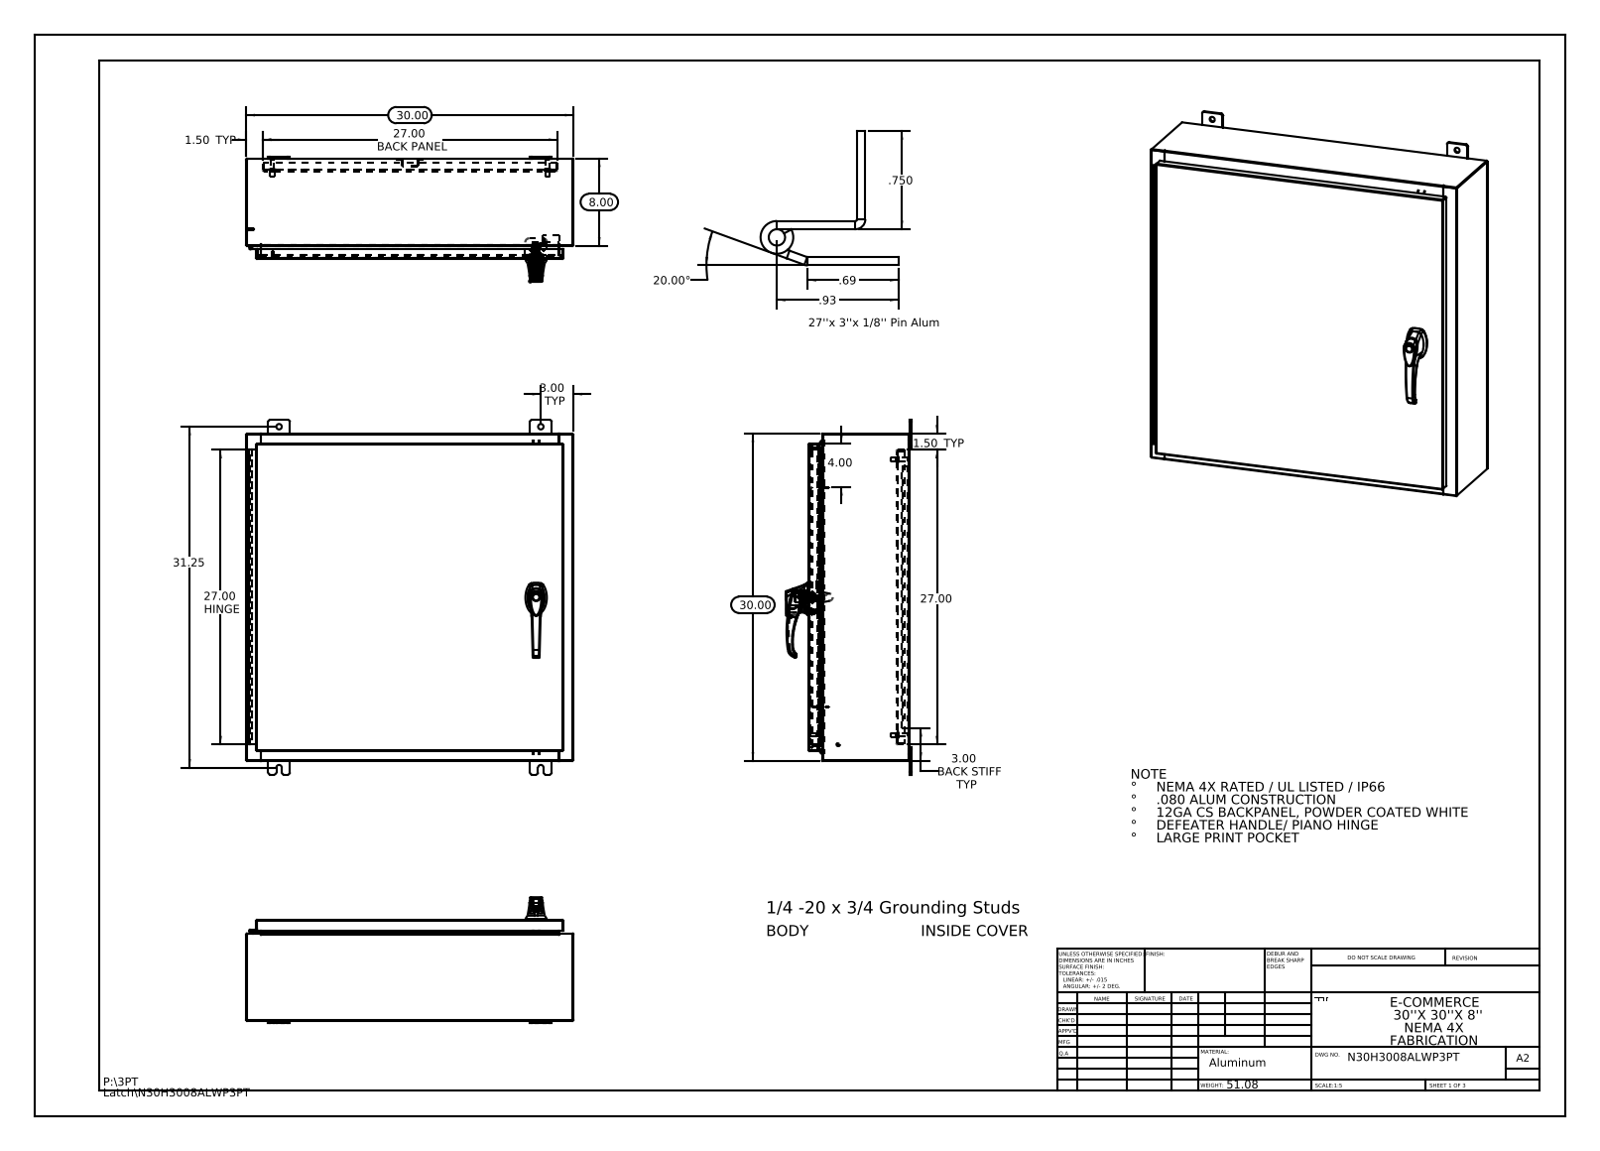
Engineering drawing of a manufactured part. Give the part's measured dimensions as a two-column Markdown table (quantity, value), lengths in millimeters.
| quantity | value |
| --- | --- |
| part name | N30H3008ALWP3PT Bottom; N30H3008ALWP3PT Mounting Studs; 00005090; N30H3008ALWP3PT 263033_Industrilas (+8 more) |
| STEP written by | SolidWorks 2013 (CONFIG_CONTROL_DESIGN) |
| units | millimeters |
| bodies | 38 solids, 2700 faces (1001 planar, 1001 cylindrical, 698 other) |
| overall size | 825.5 × 762 × 292 |
| volume | 5 444 000 mm³ |
| surface area | 5 290 000 mm² |
| round holes (diameter × count) | 12.7 × 8, 6.4 × 4, 3.5 × 3, 4.1 × 3, 2 × 2, 5.2 × 2, 8 × 2, 11.1 × 2, 3.2 × 1, 3.2 × 1, 5 × 1, 7 × 1 |
| round bosses / shafts (diameter × count) | 15.9 × 4, 9.5 × 4, 8.4 × 4, 4 × 4, 3.6 × 4, 8 × 3, 6 × 3, 30 × 1 |
| partial cylindrical surfaces (radius × count) | 3 × 37, 0.2 × 33, 0.3 × 28, 4.8 × 24, 2.2 × 22, 1 × 15, 0.7 × 12, 0.2 × 6 |
| main face-to-face distances | 1.9, 231.8, 760.1, 229.9, 2.6, 233.7, 25.4, 206.4, 27.3, 204.5 |
| hole center spacings | 212.6, 7.5, 15.9, 21.4, 31.8, 33.4, 39.6, 47.2 |
